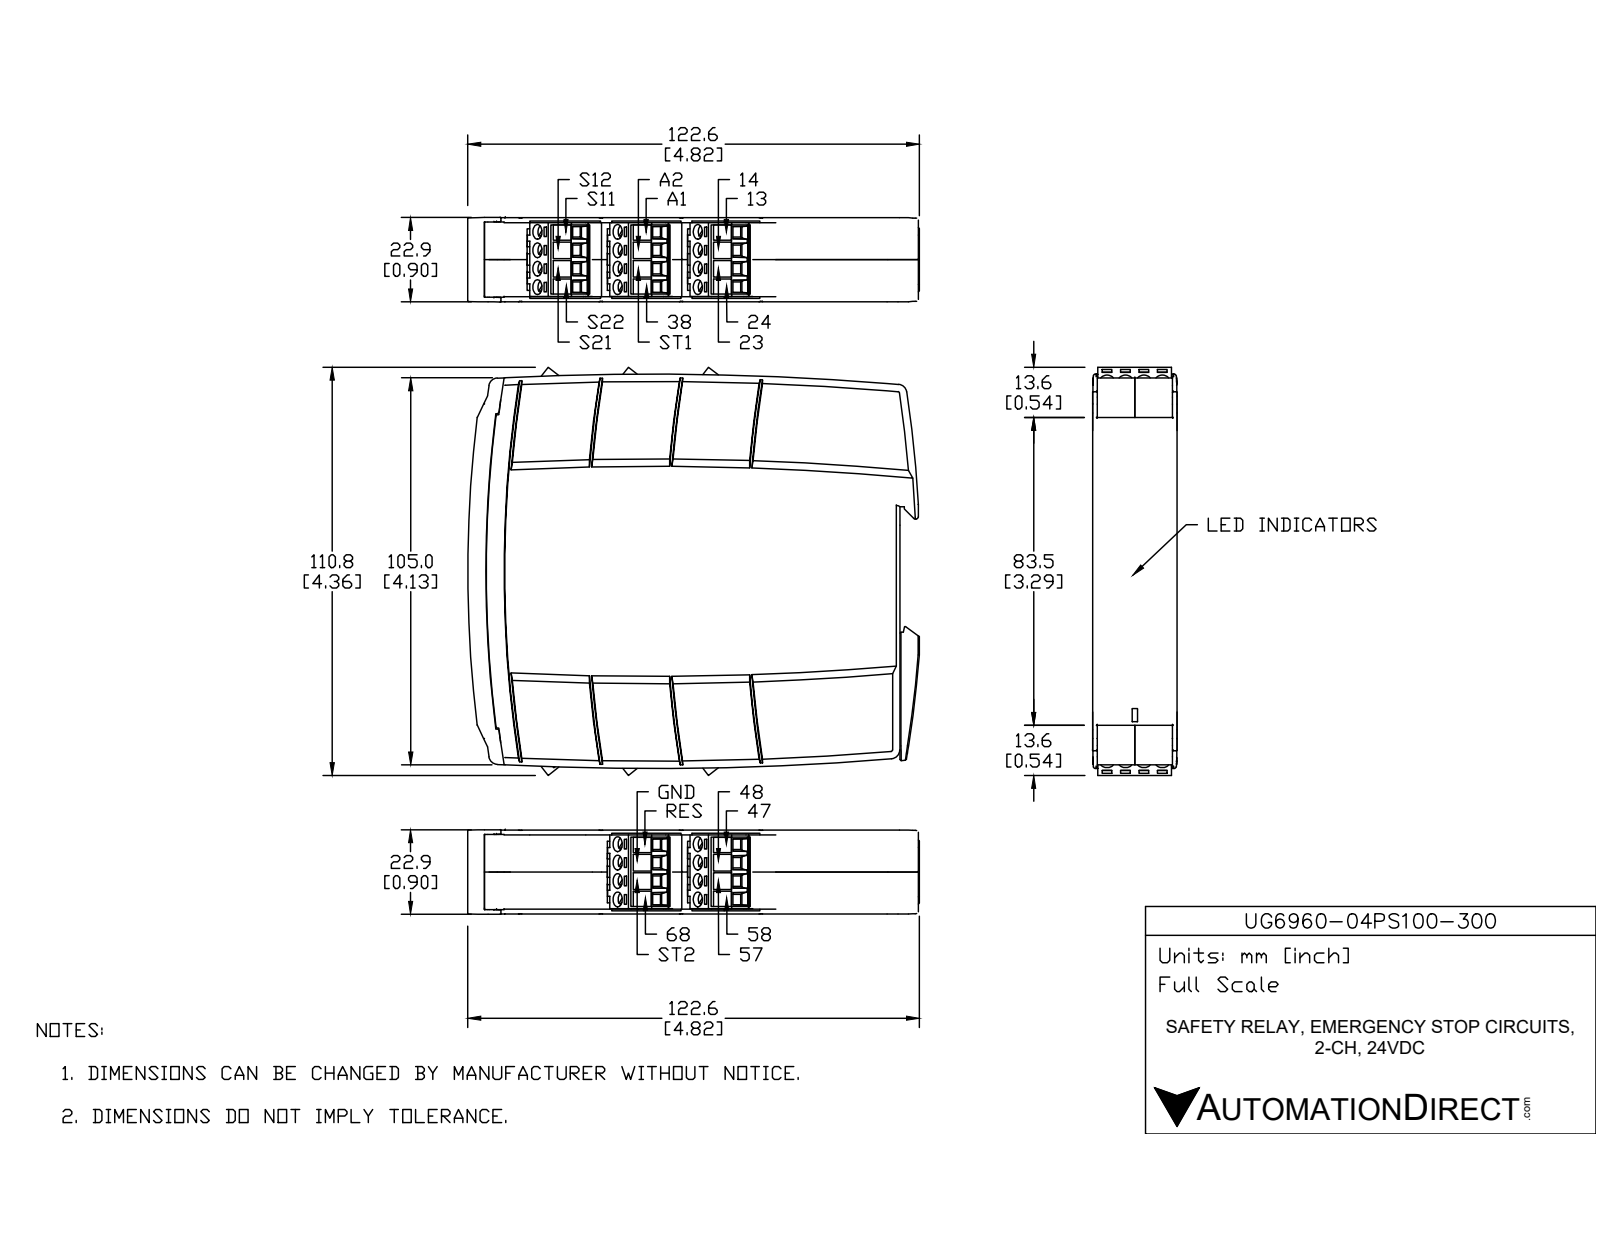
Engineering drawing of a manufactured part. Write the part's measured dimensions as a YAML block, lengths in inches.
part_name: "UG6960-04PS100-300"
step_written_by: "SolidWorks 2018 (AUTOMOTIVE_DESIGN)"
units: inches
bodies: {solids: 1, faces: 492, planar: 436, cylindrical: 47, other: 9}
overall_size: [4.813, 4.355, 0.886]
volume: 16.65
surface_area: 59.5
round_holes:
  - {diameter: 0.157, count: 20}
partial_cylinders:
  - {radius: 0.012, count: 12}
  - {radius: 0.094, count: 6}
  - {radius: 0.02, count: 2}
  - {radius: 31.496, count: 2}
  - {radius: 25.414, count: 1}
face_to_face_distances: [0.886, 0.675, 0.049, 0.837, 0.528, 0.528, 0.787, 0.567, 1.35, 0.591]
hole_center_spacings: [0.197, 0.563, 0.394, 0.528, 0.659, 0.563, 1.074, 0.591]
